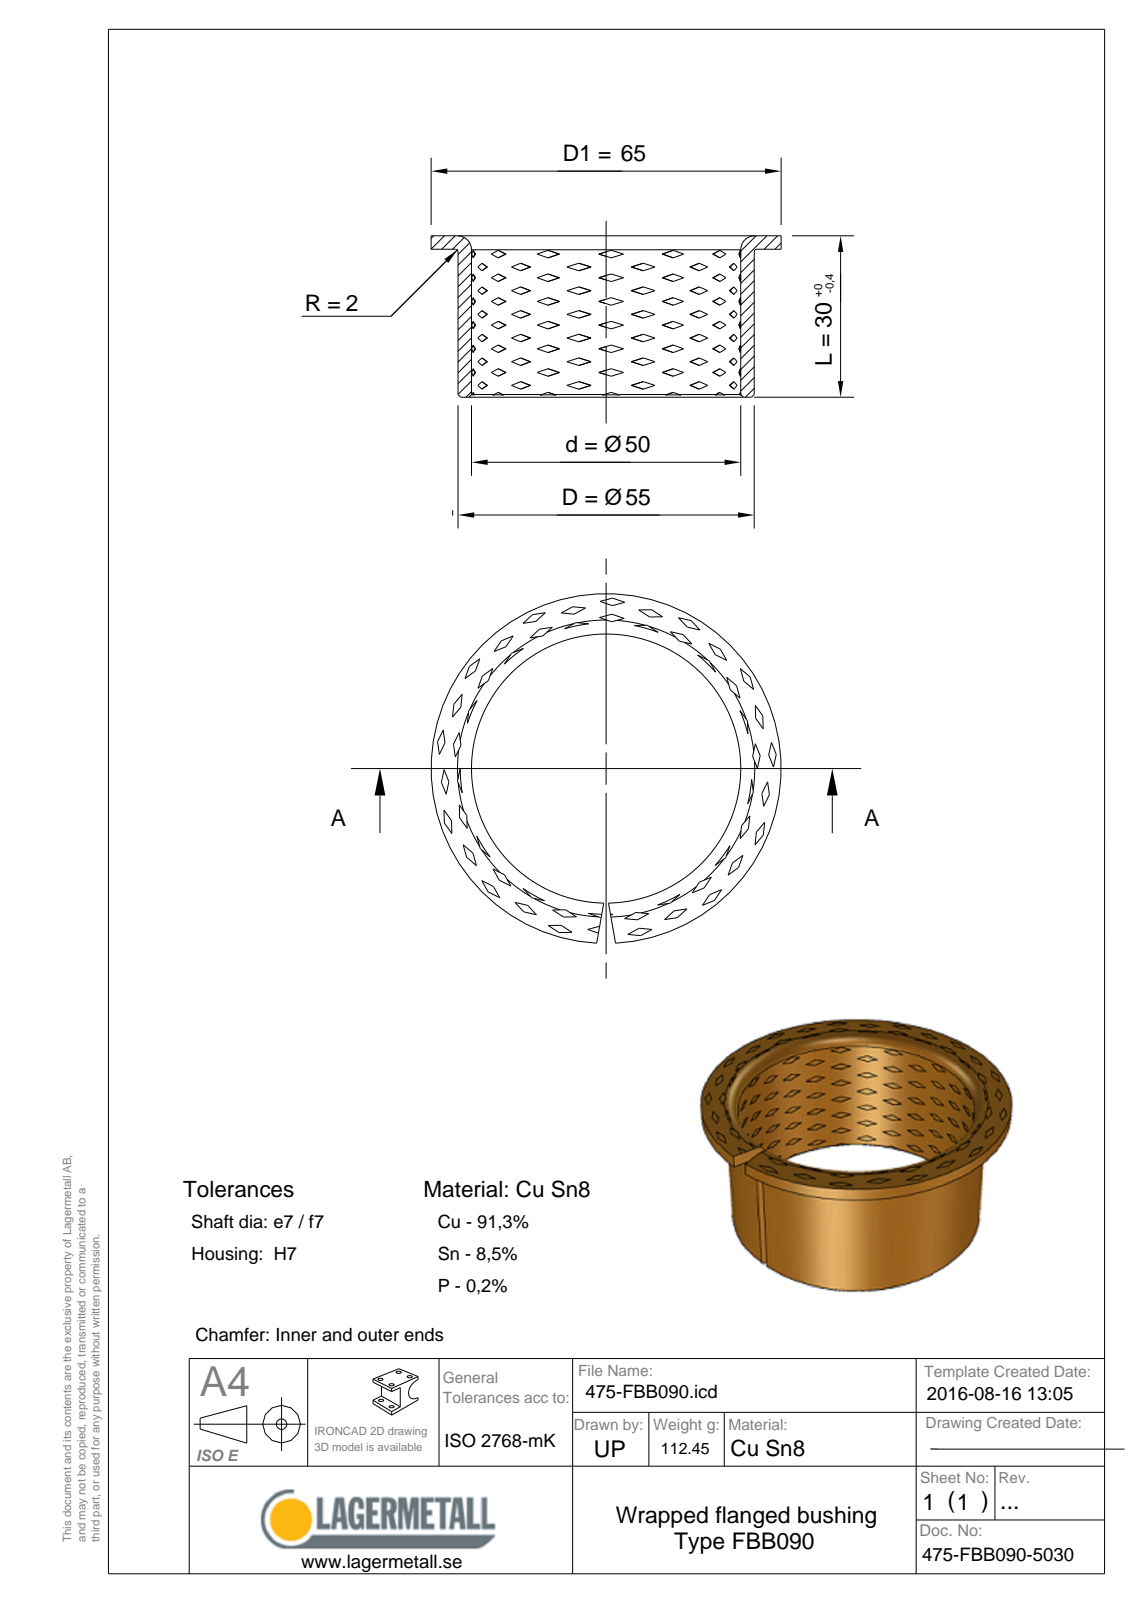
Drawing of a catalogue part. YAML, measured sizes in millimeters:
part_name: "475-FBB090-5030"
step_written_by: "Spatial InterOp 3D (CONFIG_CONTROL_DESIGN)"
units: millimeters
bodies: {solids: 1, faces: 12, planar: 5, cylindrical: 3, other: 4}
overall_size: [65, 64.95, 30]
volume: 13882
surface_area: 12128
round_holes:
  - {diameter: 50, count: 1}
round_bosses_or_shafts:
  - {diameter: 65, count: 1}
  - {diameter: 55, count: 1}
face_to_face_distances: [2.5, 27.5, 30]
